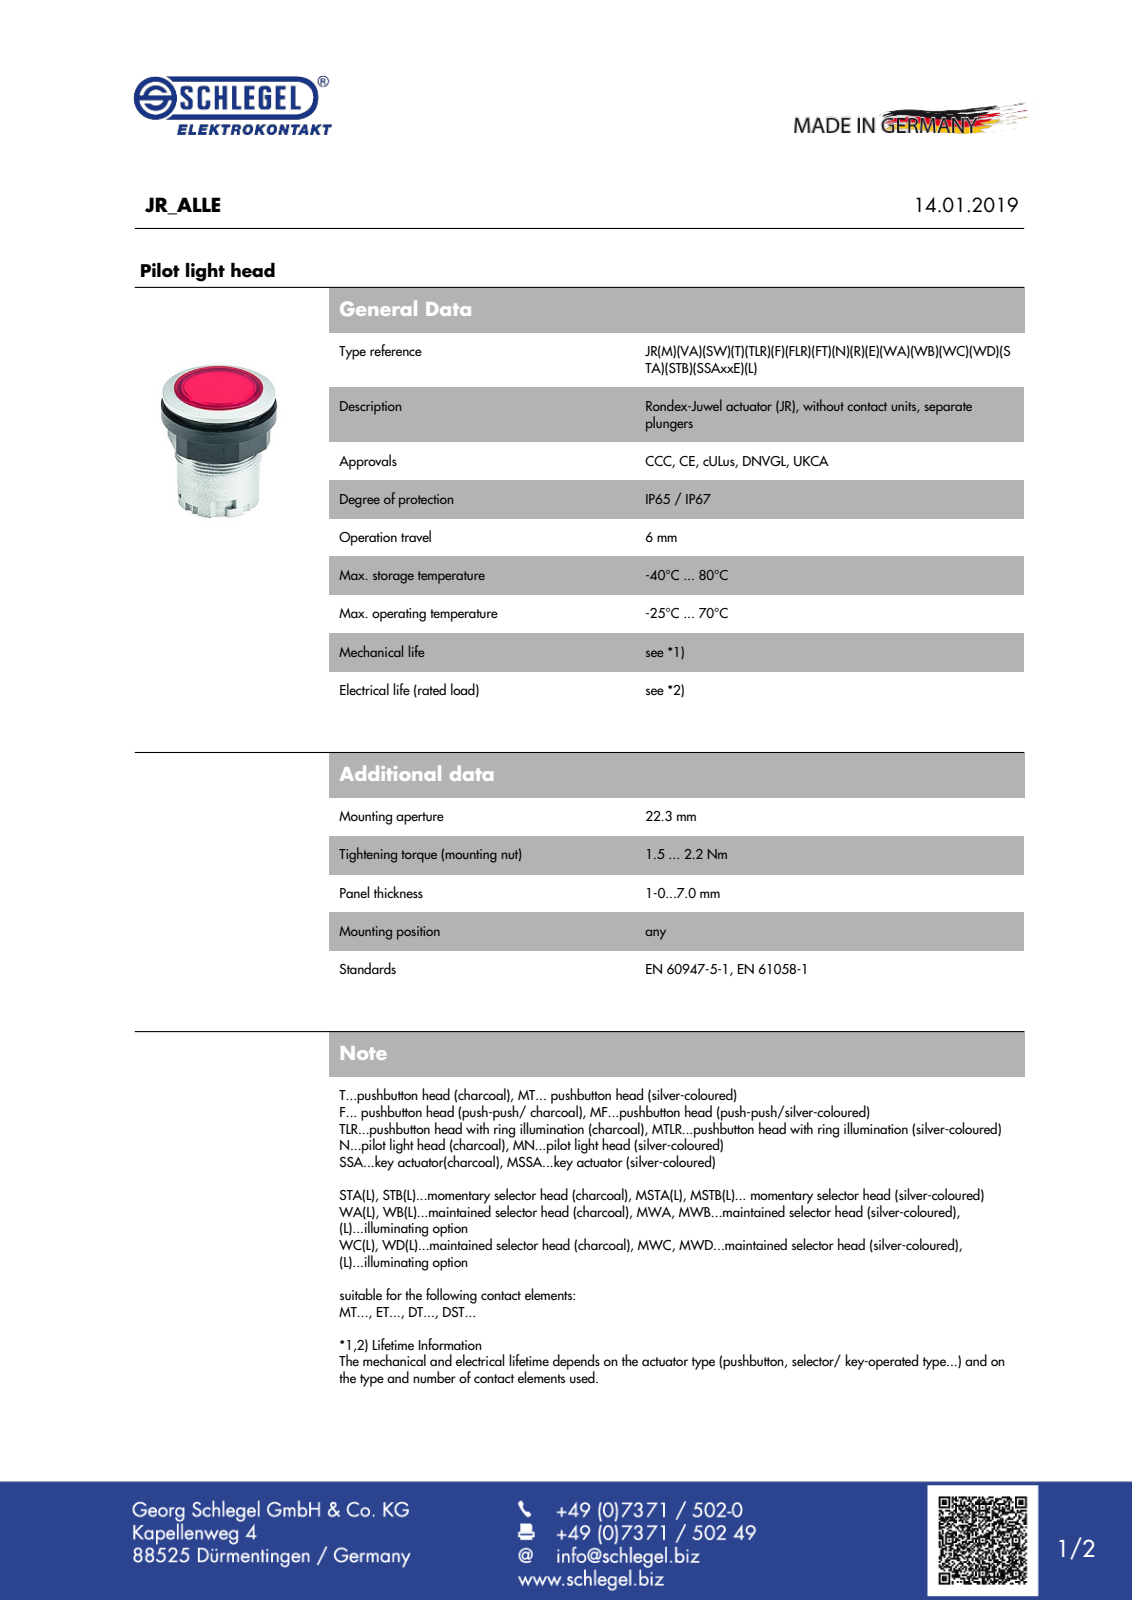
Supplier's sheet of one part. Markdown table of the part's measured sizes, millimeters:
| quantity | value |
| --- | --- |
| part name | JRN |
| STEP written by | Autodesk Inventor 2019 (AUTOMOTIVE_DESIGN) |
| units | millimeters |
| bodies | 1 solid, 341 faces (154 planar, 139 cylindrical, 48 other) |
| overall size | 33.49 × 29 × 29 |
| volume | 12 700 mm³ |
| surface area | 8 926 mm² |
| round holes (diameter × count) | 17.1 × 1, 18.6 × 1, 20.05 × 1, 22.5 × 1, 25.3 × 1 |
| round bosses / shafts (diameter × count) | 29 × 1, 27.9 × 1, 27.4 × 1, 22.2 × 1, 22.05 × 1, 20.75 × 1, 19.7 × 1, 18.3 × 1 |
| partial cylindrical surfaces (radius × count) | 0.2 × 20, 0.6 × 18, 0.5 × 16, 0.35 × 8, 1.1 × 6, 0.8 × 4, 0.3 × 2, 1 × 2 |
| main face-to-face distances | 6.5, 31.2, 24, 3, 29, 2.2, 3.5, 26, 5.2, 22.5 |
